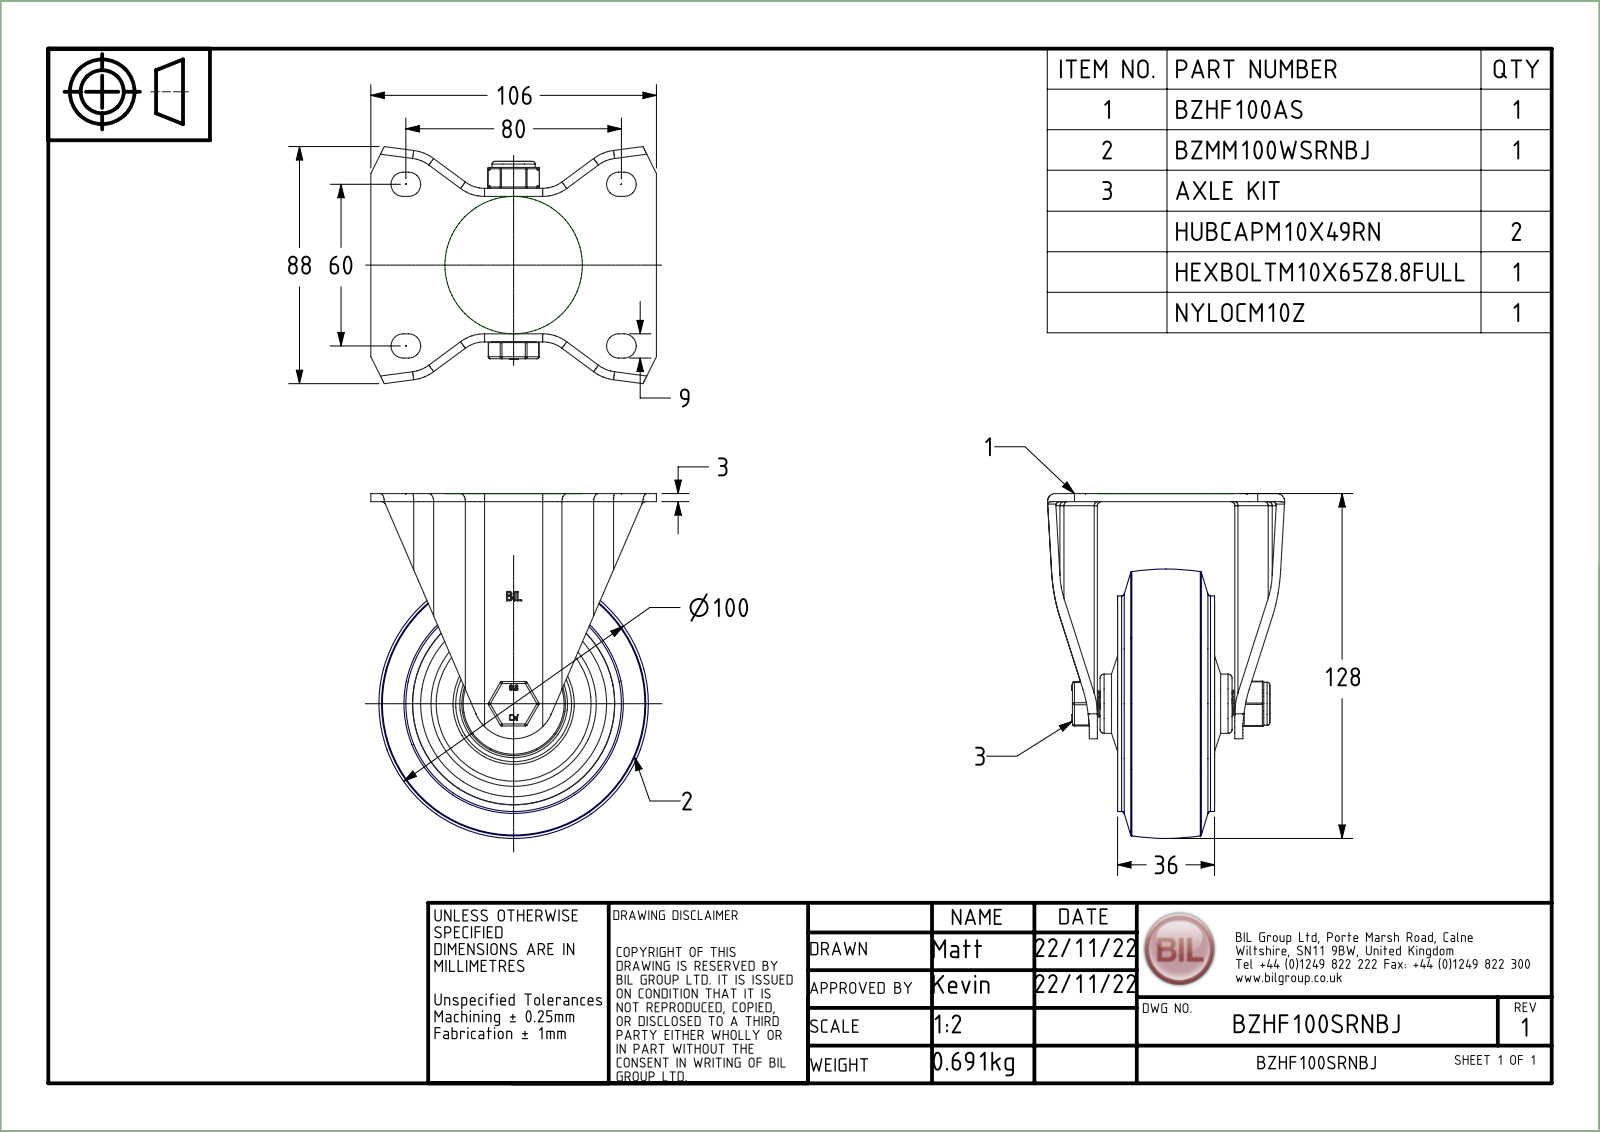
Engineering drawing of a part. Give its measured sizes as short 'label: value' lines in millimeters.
name: BZHF100AS; ZINC PLATED, PRESSED STEEL BRACKET; BZHF100SRNBJ; BZMM100WSRNBJ (+7 more)
written by: Spatial InterOp 3D (AUTOMOTIVE_DESIGN)
unit: mm
bodies: 21 solids, 1042 faces (286 planar, 400 cylindrical, 356 other)
size: 128 × 106 × 88
volume: 243 433 mm³; area: 119 161 mm²
holes: 1× ⌀10, 1× ⌀10.2, 1× ⌀10.25, 1× ⌀12, 1× ⌀15, 1× ⌀20, 1× ⌀22.5, 1× ⌀26, 1× ⌀30, 1× ⌀31, 1× ⌀32, 1× ⌀33
bosses: 1× ⌀80, 1× ⌀43, 1× ⌀38.5, 1× ⌀35, 1× ⌀30.5, 1× ⌀28, 1× ⌀23, 1× ⌀22
rounds: 18× R0.5, 12× R0.75, 12× R1.5, 10× R3, 8× R4.5, 5× R12, 4× R6, 4× R8
face distances: 3, 54, 10.5, 3.01, 25.27, 7.5, 46.5, 43.5, 25.5, 22.5
